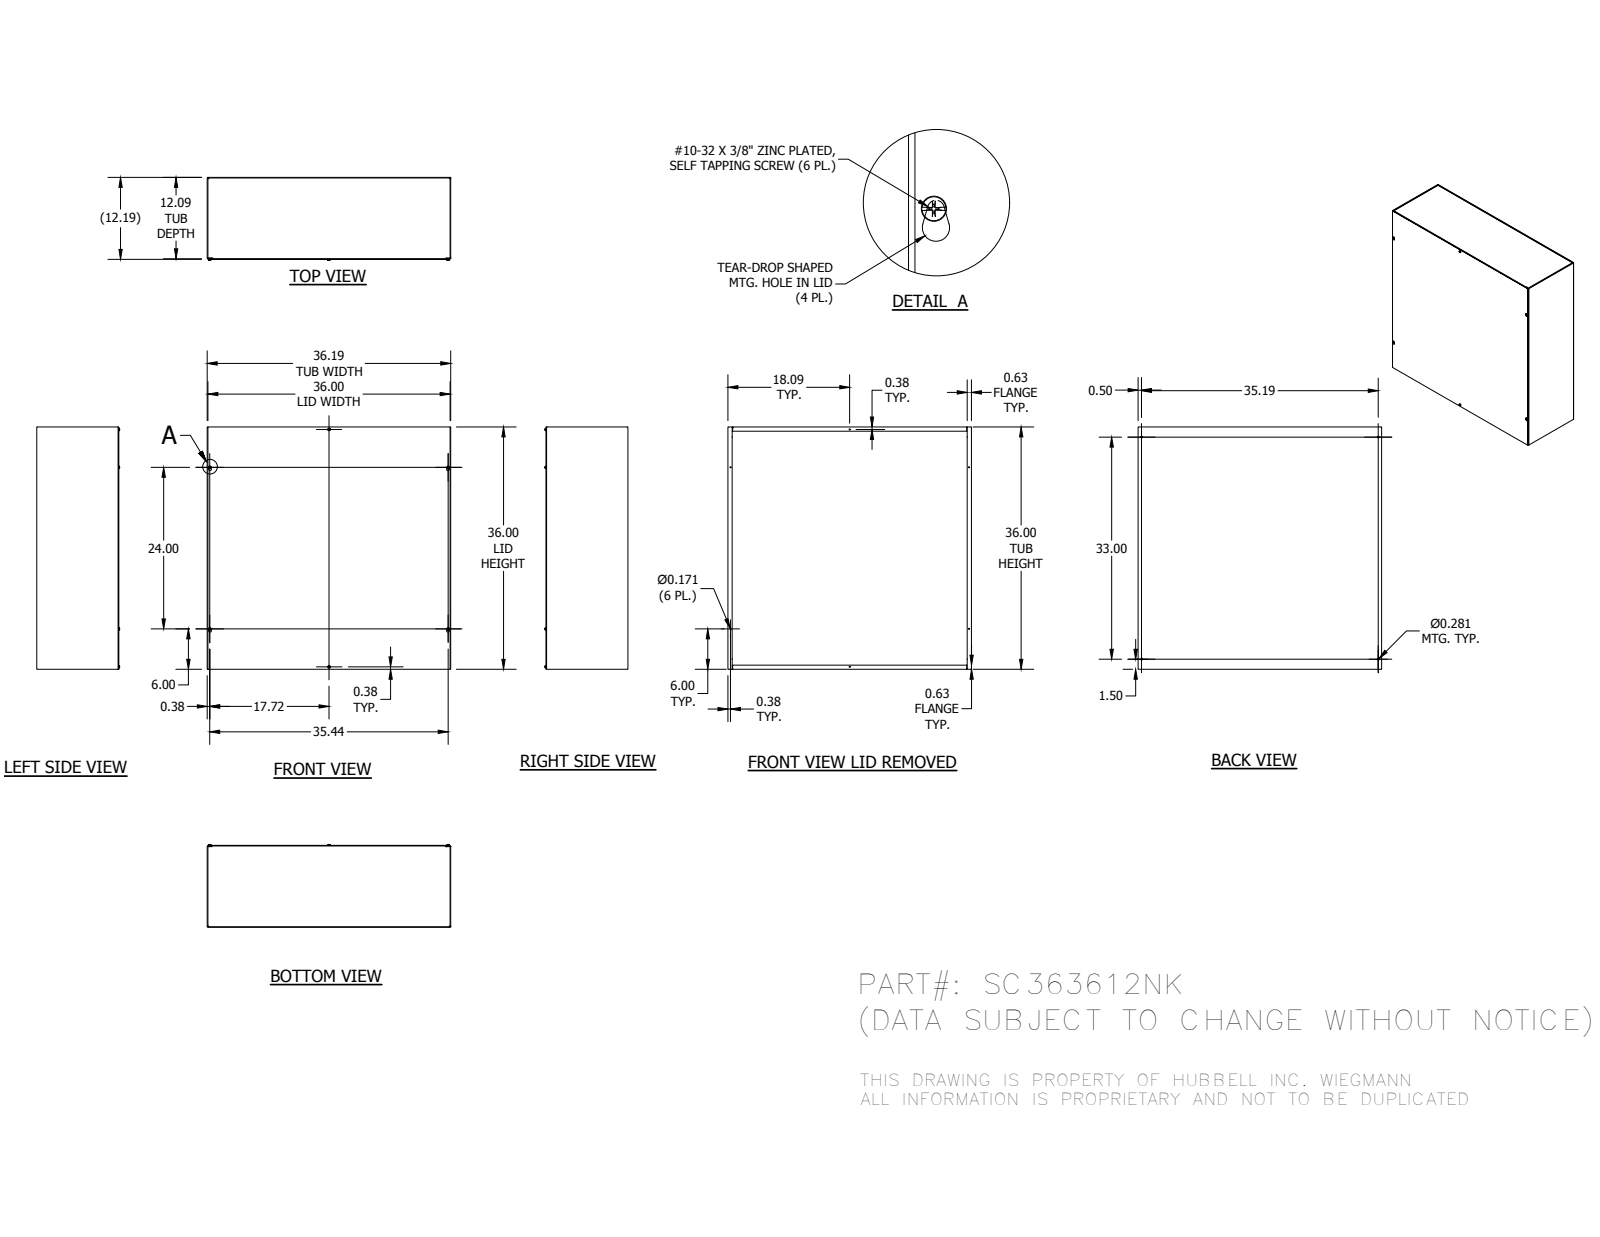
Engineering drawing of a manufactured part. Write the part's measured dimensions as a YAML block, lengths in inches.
part_name: "SC363612NKBLR; SC3612NKTB; SC3636LPA; 37214 (+1 more)"
step_written_by: "Autodesk Inventor 2014 (AUTOMOTIVE_DESIGN)"
units: inches
bodies: {solids: 10, faces: 404, planar: 232, cylindrical: 50, other: 122}
overall_size: [36.187, 36, 12.319]
volume: 417.7
surface_area: 8965
round_holes:
  - {diameter: 0.171, count: 6}
  - {diameter: 0.281, count: 4}
  - {diameter: 0.312, count: 2}
round_bosses_or_shafts:
  - {diameter: 0.19, count: 6}
partial_cylinders:
  - {radius: 0.016, count: 12}
  - {radius: 0.109, count: 12}
  - {radius: 0.125, count: 4}
  - {radius: 0.203, count: 4}
face_to_face_distances: [0.094, 12.094, 12, 12.187, 36, 35.906, 36.094, 35.813, 36.187, 0.187]
hole_center_spacings: [4.502, 17.63, 18.59, 28.5, 34.519, 35.598, 38.393, 45.379]
